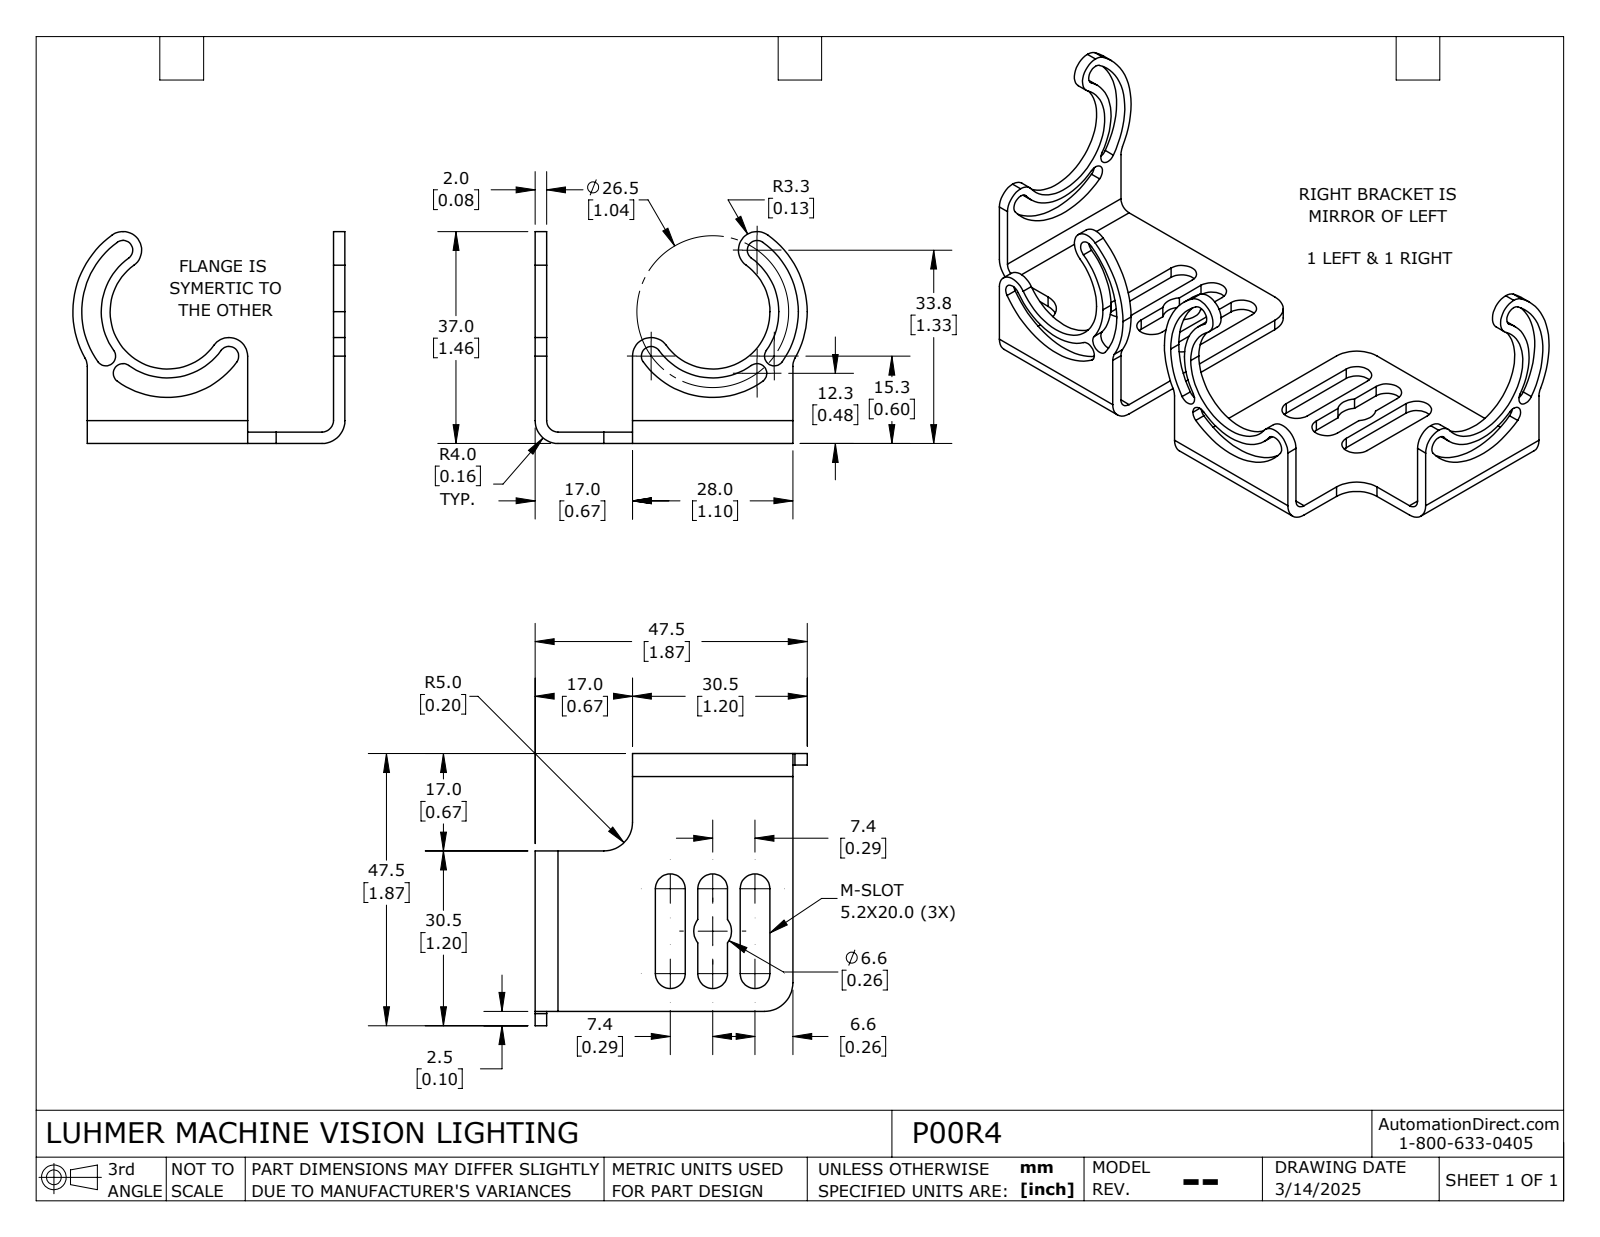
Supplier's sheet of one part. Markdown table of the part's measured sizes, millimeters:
| quantity | value |
| --- | --- |
| part name | P00R4 |
| STEP written by | SolidWorks 2024 (AUTOMOTIVE_DESIGN) |
| units | millimeters |
| bodies | 2 solids, 136 faces (36 planar, 100 cylindrical, 0 other) |
| overall size | 105.2 × 47.5 × 37 |
| volume | 8 360 mm³ |
| surface area | 11 030 mm² |
| partial cylindrical surfaces (radius × count) | 1.7 × 12, 2.6 × 12, 3.3 × 6, 5 × 4, 2 × 3, 3 × 3, 4 × 3, 10 × 3 |
| main face-to-face distances | 2, 103.3, 43, 45, 105.2, 101.2, 43.2, 60.2, 58.2, 28 |
